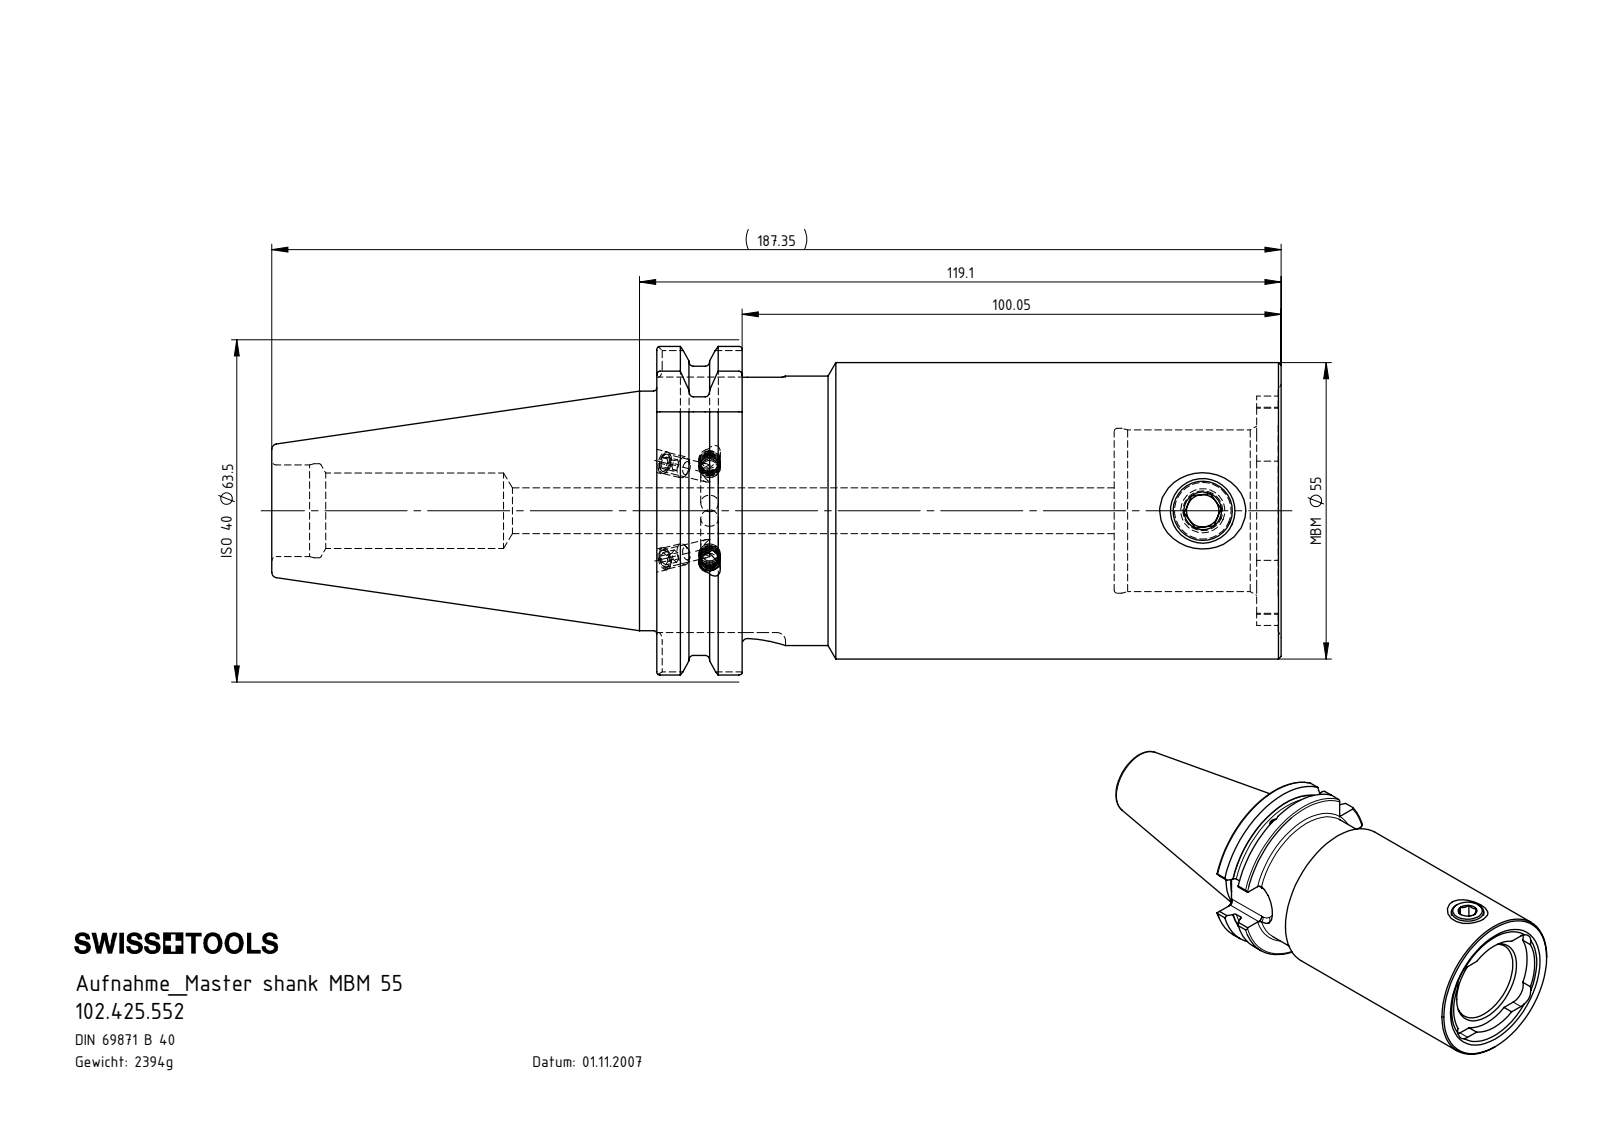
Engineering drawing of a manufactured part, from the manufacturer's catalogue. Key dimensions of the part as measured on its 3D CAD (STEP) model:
Part name (STEP PRODUCT): SB4-MB5.K01.119_D_mit Bundkhlung; MB5-ER1.001.017_A; ISO 4026 - M4 x 5_PreviewCfg; KVT_MB_600_040 (+1 more)
STEP written by: SolidWorks 2017 (CONFIG_CONTROL_DESIGN)
Units: millimetres
Bodies: 8 solids, 318 faces (81 planar, 96 cylindrical, 141 other)
Overall size (bounding box): 187.35 × 63.5 × 60.94
Volume: 304 919 mm³ · Surface area: 44 245 mm²
Round holes (diameter × count): ⌀3.3 ×3, ⌀3 ×2, ⌀4.2 ×2, ⌀4 ×1, ⌀6 ×1, ⌀8.5 ×1, ⌀11 ×1, ⌀14 ×1, ⌀17 ×1, ⌀17.45 ×1, ⌀30 ×1, ⌀30.6 ×1
Round bosses / shafts (diameter × count): ⌀4 ×4, ⌀55 ×1, ⌀50 ×1, ⌀44.45 ×1, ⌀12 ×1
Partial cylindrical surfaces — rounded edges, fillets, slot ends (radius × count): R1.6 ×8, R5.2 ×4, R8 ×1, R8.05 ×1, R18.5 ×1, R21.27 ×1, R28 ×1, R31.75 ×1
Main face-to-face distances: 15.85, 84.9, 69.05, 115.9, 100.05, 31, 111.35, 95.5, 26.45, 4.55
